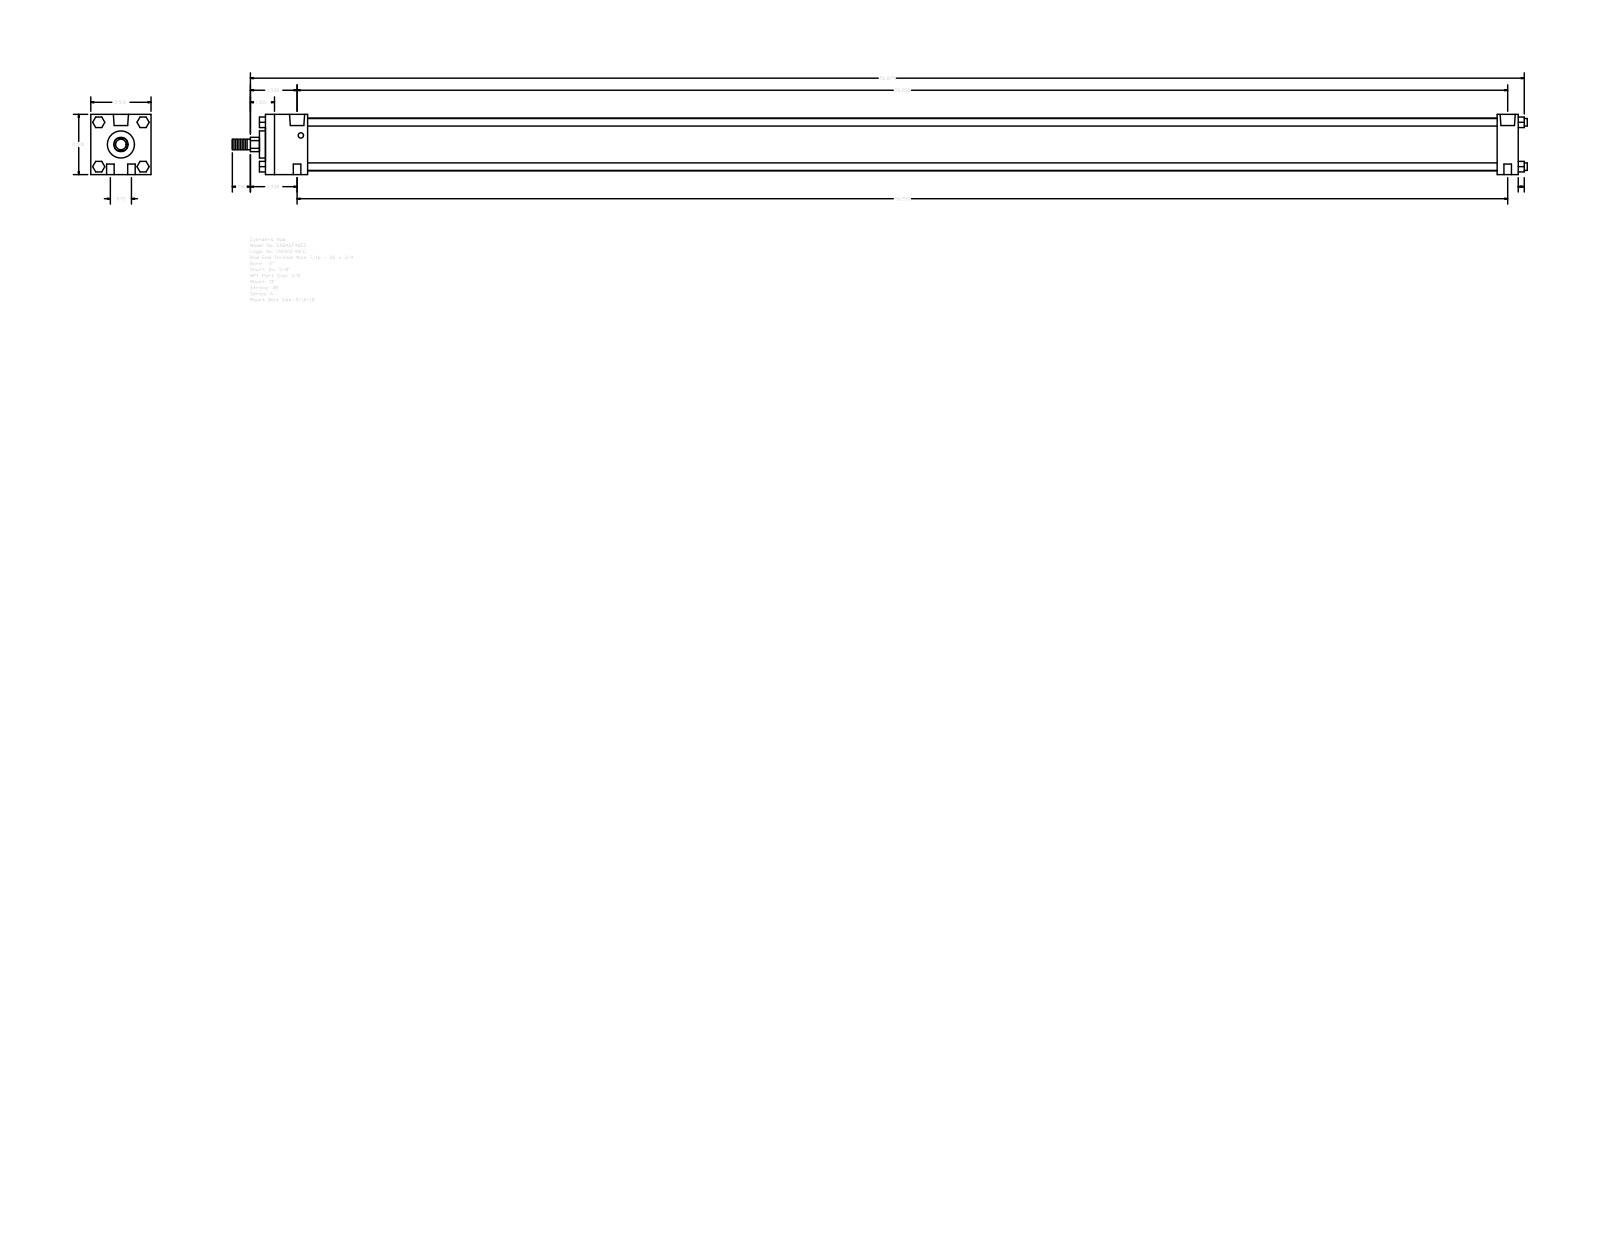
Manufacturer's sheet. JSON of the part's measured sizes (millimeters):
{"part_name": "A_SF__0200_0.625", "step_written_by": "GSSL Pune (CONFIG_CONTROL_DESIGN)", "units": "millimeters", "bodies": {"solids": 0, "faces": 124, "planar": 94, "cylindrical": 30, "other": 0}, "overall_size": [1365.25, 63.5, 63.5], "round_holes": [[7.94, 4], [5.56, 2], [15.93, 2]], "round_bosses_or_shafts": [[7.94, 4], [55.63, 1], [28.57, 1], [15.88, 1], [11.11, 1]], "partial_cylinders_radius": [[7.54, 1]], "face_to_face_distances": [63.5, 1320.79, 1298.57, 22.22, 44.45, 1254.12, 1276.34, 50.8, 6.35, 1304.92], "hole_center_spacings": [11.11, 1276.4, 1276.35, 22.22, 1276.54, 1268.4]}
